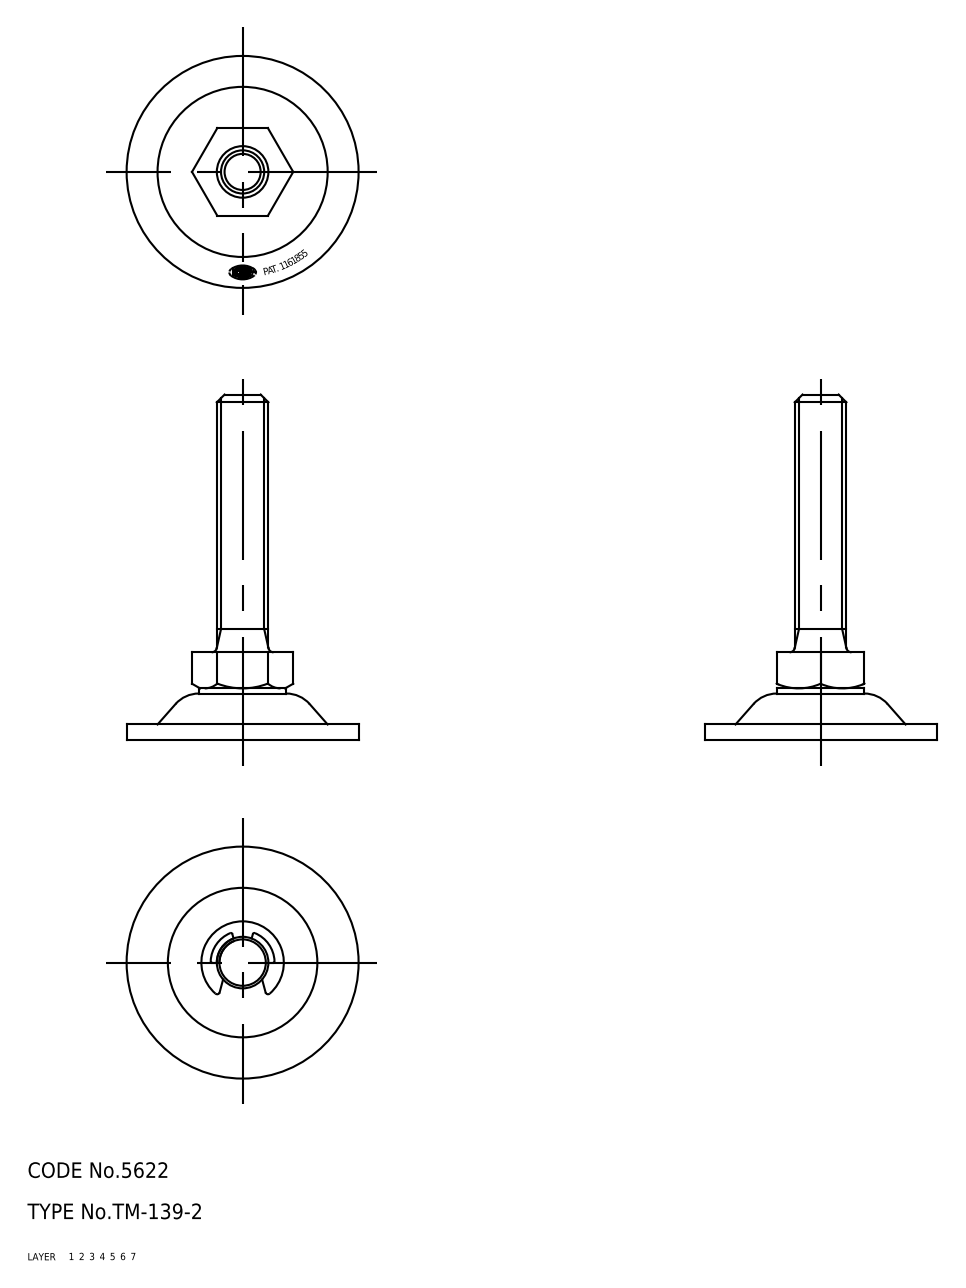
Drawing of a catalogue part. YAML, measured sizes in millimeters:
part_name: "washer; retainer; foot; bolt (+1 more)"
step_written_by: "CADfix (AUTOMOTIVE_DESIGN)"
units: millimeters
bodies: {solids: 4, faces: 76, planar: 0, cylindrical: 0, other: 76}
overall_size: [67, 45, 45]
volume: 11522
surface_area: 7233
